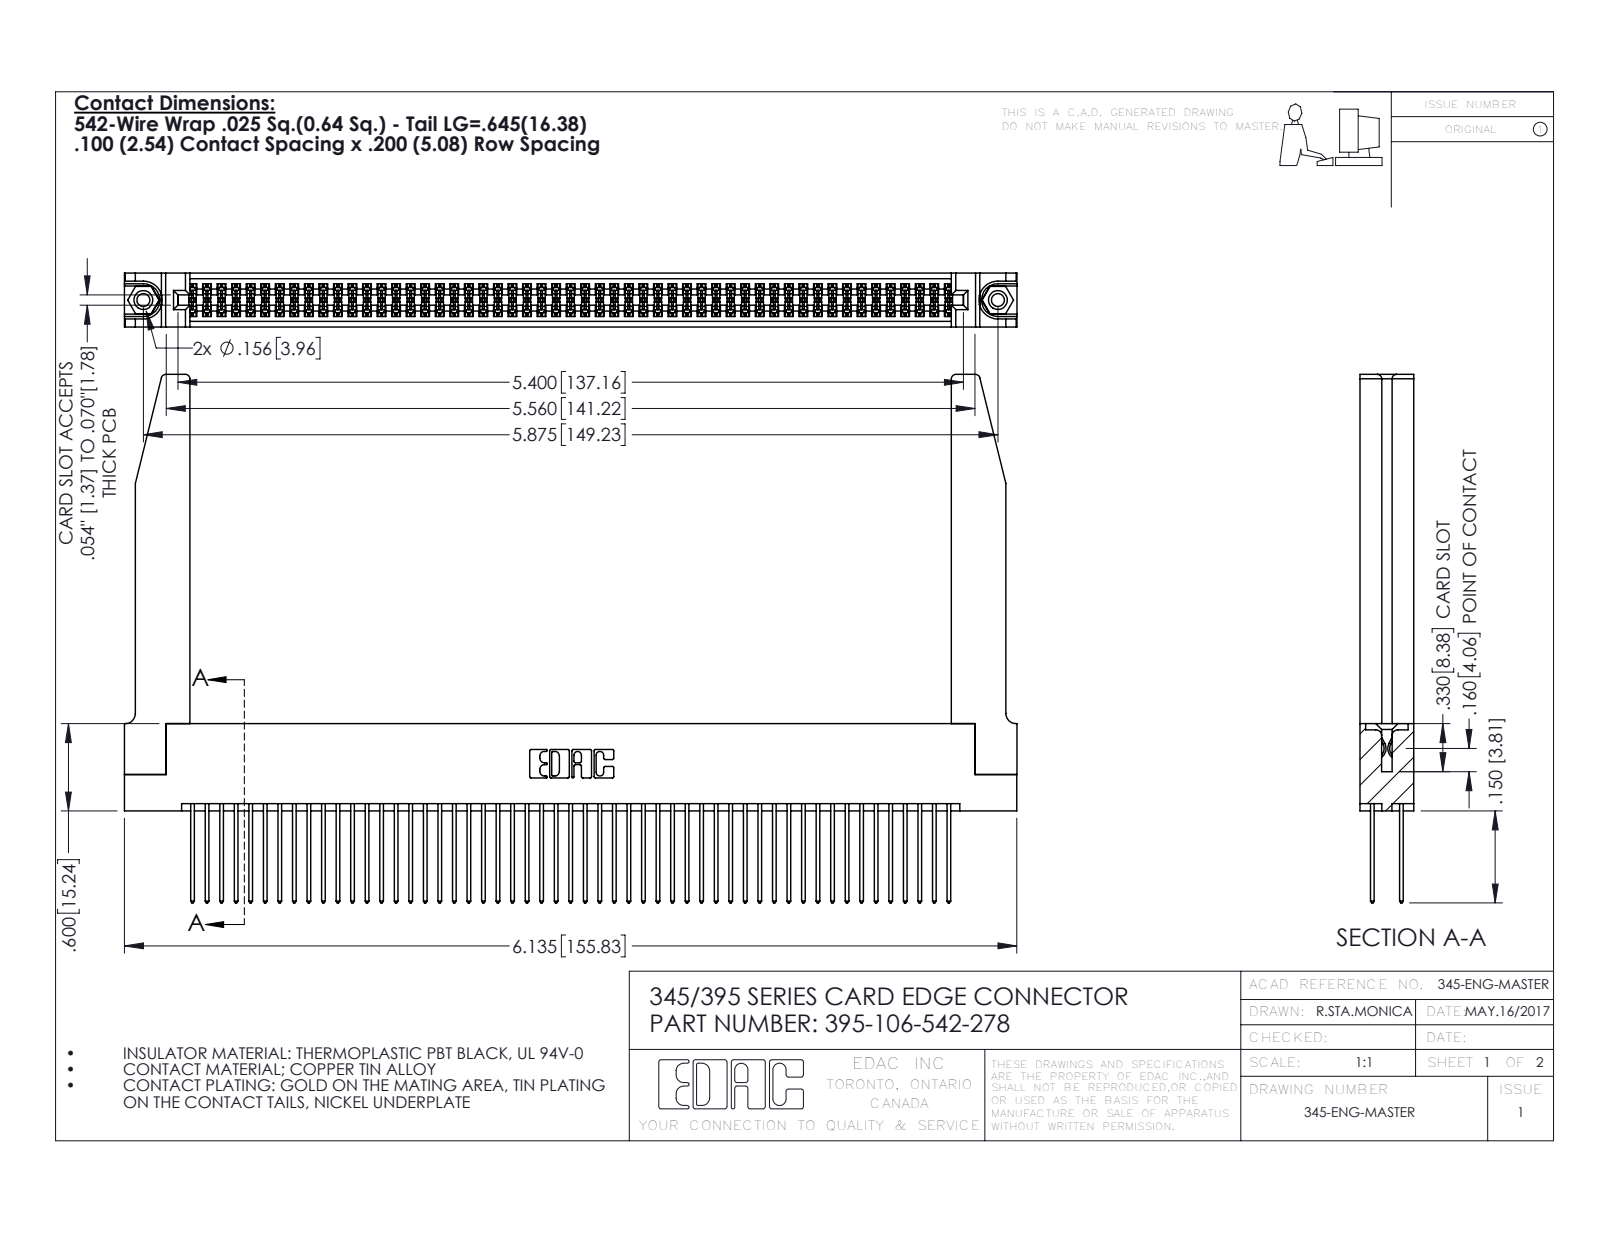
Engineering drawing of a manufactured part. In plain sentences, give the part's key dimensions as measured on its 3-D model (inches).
The part is named "345-250-001_345-250-001-102; 345-220-078_345-220-078; 345 Part_Flush Mounting Lugs - 0.156 Dia-TH; 395-106-542-278 (+1 more)". Its 3-D file was written by "SolidWorks 2016 (CONFIG_CONTROL_DESIGN)". It is 111 solids with 5660 faces: 3720 planar, 1888 cylindrical and 52 other. Overall it measures 6.136 by 3.632 by 0.37 inches. Its volume is 1.434 cubic inches and its surface area 50.56 square inches. Round holes: 2 of diameter 0.089, 2 of diameter 0.125, 2 of diameter 0.156, 1 of diameter 0.064. Round bosses or shafts: 2 of diameter 0.155. Partial cylindrical surfaces (rounded edges, fillets, slot ends): 159 of radius 0.006, 106 of radius 0.01, 22 of radius 0.01, 8 of radius 0.03, 6 of radius 0.007, 6 of radius 0.031, 3 of radius 0.026, 2 of radius 0.014. The main face-to-face distances are 0.072, 0.298, 0.37, 0.2, 0.098, 0.272, 0.025, 0.225, 0.175, 0.148. The hole center spacings are 0.27, 5.639, 5.875.
